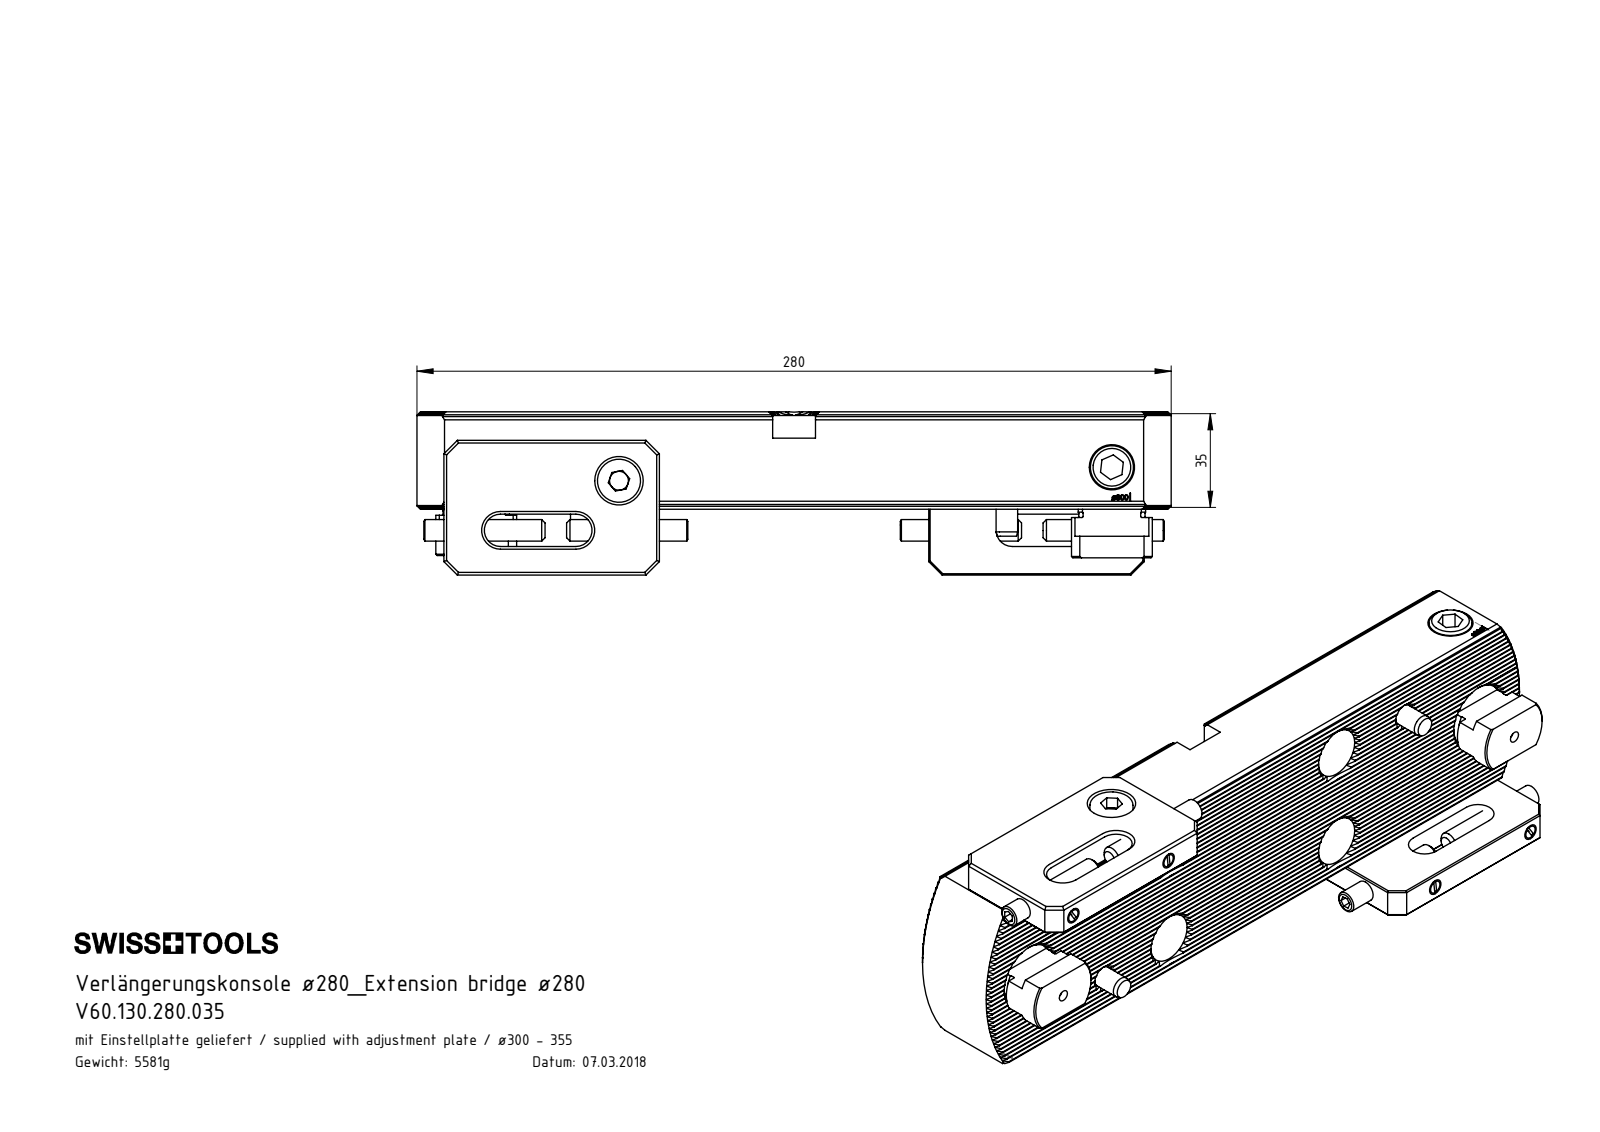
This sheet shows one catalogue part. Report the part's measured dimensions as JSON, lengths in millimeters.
{"part_name": "ISO 4766 - M6x12_ISO 4766 - M6 x 10; VK1-ER7.001.012_B; DIN 7984 - M10 x 16; Ko1-VK1.280.035_D (+8 more)", "step_written_by": "SolidWorks 2017 (AUTOMOTIVE_DESIGN)", "units": "millimeters", "bodies": {"solids": 27, "faces": 1499, "planar": 975, "cylindrical": 299, "other": 225}, "overall_size": [280, 94, 60.58], "volume_mm3": 716992, "surface_area_mm2": 152062, "round_holes": [[5, 4], [6, 4], [6.8, 4], [13, 4], [19, 4], [2, 2], [8, 2], [8.5, 2], [10.5, 2], [11, 2], [14, 2], [18, 2]], "round_bosses_or_shafts": [[16, 4], [6, 4], [10, 2], [8, 2]], "partial_cylinders_radius": [[0.14, 66], [2, 8], [6, 4], [12.3, 2], [15, 2], [65, 2], [7.95, 1]], "face_to_face_distances": [70, 1.73, 12, 82, 16.64, 3.46, 51.96, 0.5, 11.5, 82.5], "hole_center_spacings": [76.66, 163.23, 236, 7.9, 18.55, 19.61, 33.42, 34.53]}
